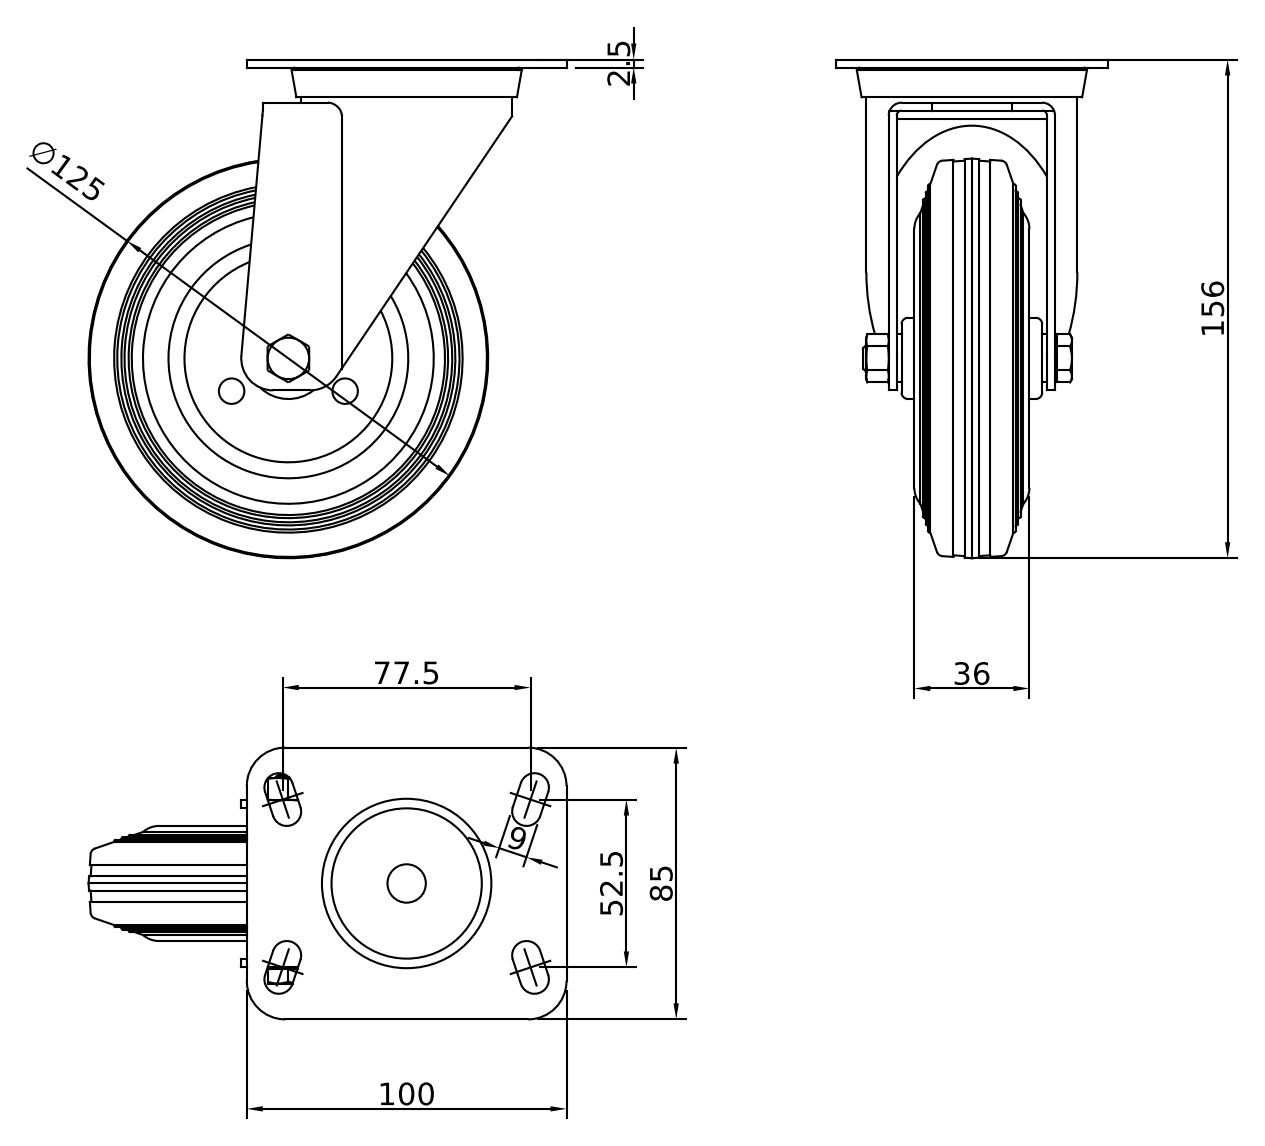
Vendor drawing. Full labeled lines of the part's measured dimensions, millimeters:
Part name (STEP PRODUCT): CRUST0000041; 440000025910; 440000025911; 440000025912 (+2 more)
STEP written by: Autodesk Inventor 2022 (AUTOMOTIVE_DESIGN)
Units: millimetres
Bodies: 5 solids, 215 faces (94 planar, 46 cylindrical, 75 other)
Overall size (bounding box): 156 × 149.5 × 85
Volume: 386 655 mm³ · Surface area: 95 139 mm²
Round holes (diameter × count): ⌀6.02 ×1, ⌀6.65 ×1, ⌀8 ×1, ⌀12 ×1, ⌀15 ×1, ⌀15.5 ×1, ⌀18 ×1, ⌀62 ×1, ⌀65 ×1
Round bosses / shafts (diameter × count): ⌀75 ×1, ⌀66 ×1, ⌀54 ×1, ⌀25.4 ×1, ⌀11.47 ×1, ⌀7.53 ×1
Partial cylindrical surfaces — rounded edges, fillets, slot ends (radius × count): R4.5 ×8, R12 ×4, R1.5 ×2, R4 ×2, R10 ×2, R0.38 ×1, R1.13 ×1
Main face-to-face distances: 2.5, 49.5, 24.8, 16, 27.2, 22.3, 24.7, 47, 52, 18.5
Hole centre spacings: 21
